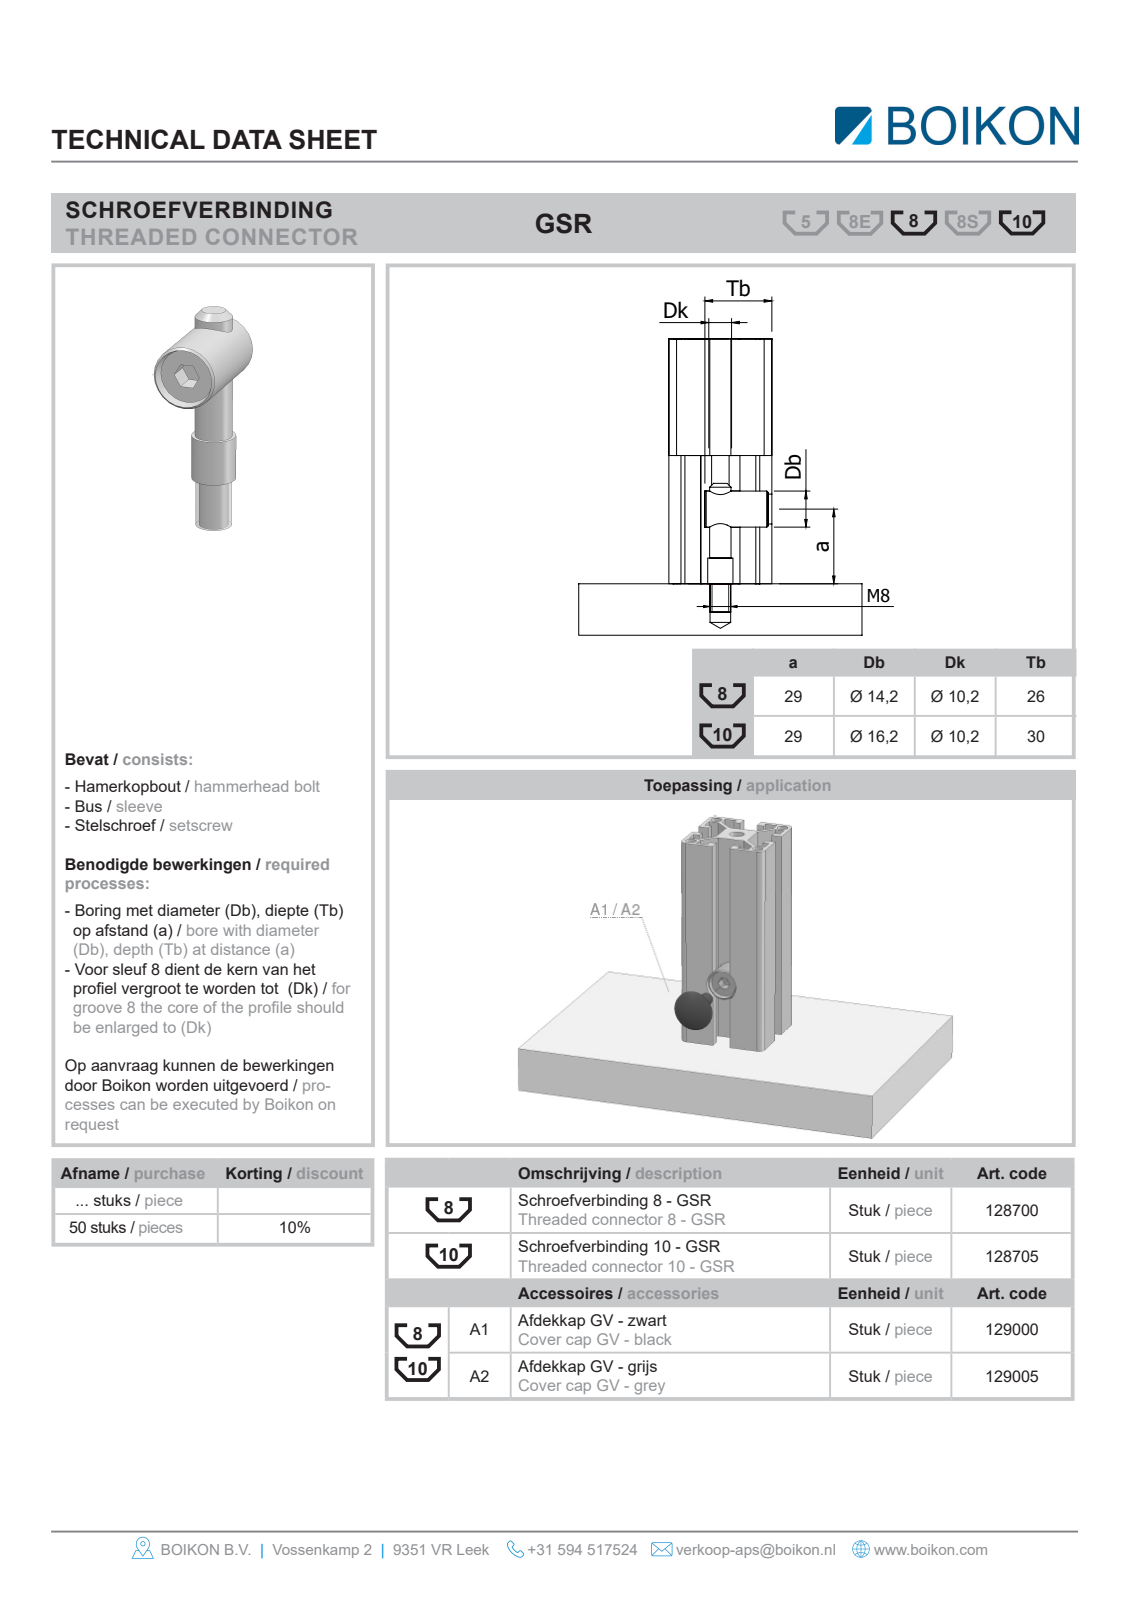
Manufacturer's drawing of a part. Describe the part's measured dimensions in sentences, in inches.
The part is named "Root; 128705Schroefverbinding 10 - GSRBOIKON". Its 3-D file was written by "HiCAD 2013 1802.4 Build 509 (AUTOMOTIVE_DESIGN)". It is 1 solid with 19 faces: 13 planar, 5 cylindrical and 1 other. Overall it measures 1.969 by 1.142 by 0.63 inches. Its volume is 0.448 cubic inches and its surface area 4.619 square inches. Round bosses or shafts: 1 of diameter 0.63, 1 of diameter 0.386, 1 of diameter 0.327, 1 of diameter 0.255. The main face-to-face distances are 1.142, 0.236, 0.394, 1.26, 1.024, 1.693, 1.457, 0.433, 0.748, 0.276.
